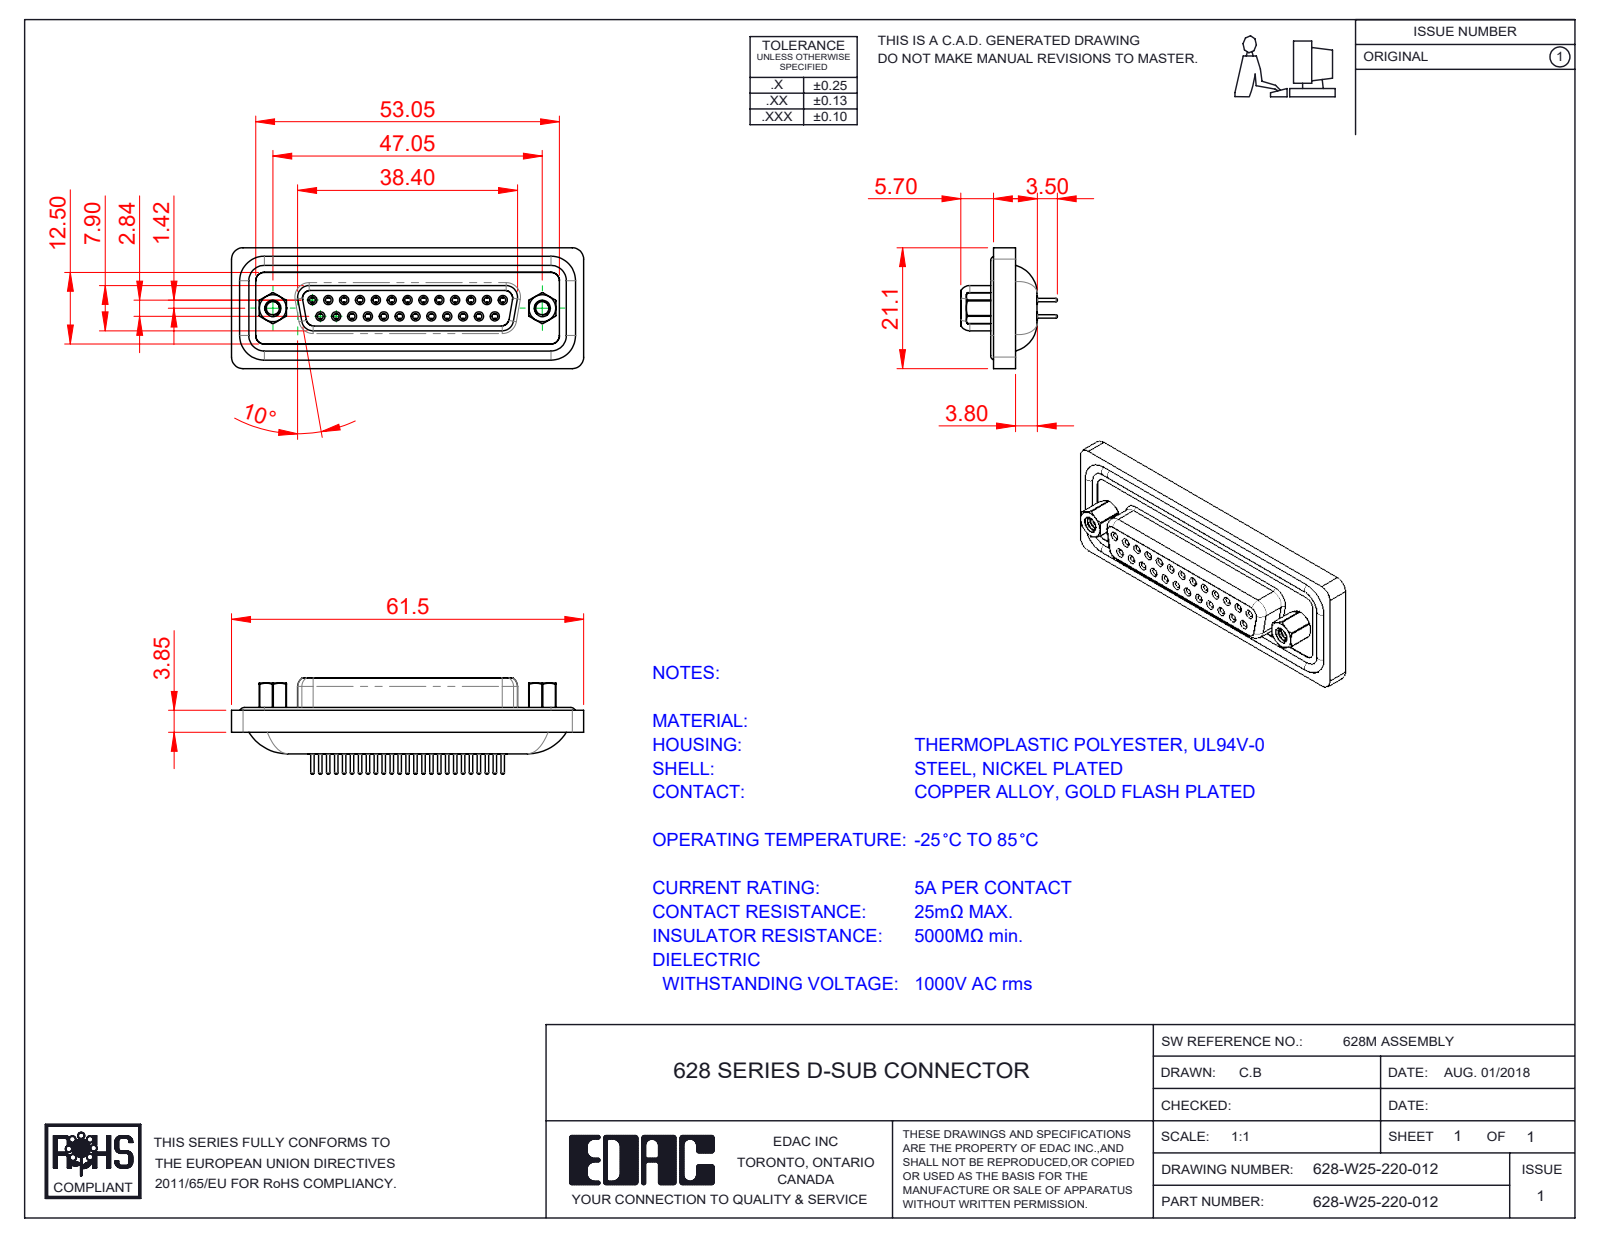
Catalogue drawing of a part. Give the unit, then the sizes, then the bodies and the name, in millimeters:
Units: millimetres
Overall size (bounding box): 61.5 × 21.1 × 16.85
Round holes (diameter × count): ⌀1 ×25, ⌀1.1 ×25, ⌀1.5 ×25, ⌀1.7 ×25, ⌀1.8 ×25, ⌀2 ×25, ⌀2.26 ×2, ⌀2.29 ×2, ⌀4 ×2, ⌀4.8 ×2, ⌀5 ×2
Round bosses / shafts (diameter × count): ⌀1.6 ×29, ⌀2.2 ×25, ⌀0.6 ×25, ⌀4.9 ×2, ⌀2.79 ×2
Partial cylindrical surfaces — rounded edges, fillets, slot ends (radius × count): R2 ×16, R1.5 ×14, R1.35 ×8, R2.7 ×6, R0.5 ×4, R0.9 ×4, R1.6 ×4, R1.75 ×4
Main face-to-face distances: 0.4, 7.45, 1.1, 2.75, 7.5, 3.75, 13.65, 0.5, 8.45, 6.2
Hole centre spacings: 3.16, 2.77, 5.54, 8.31, 11.08, 13.85, 16.62, 5.03
Volume: 8 488 mm³ · Surface area: 13 359 mm²
Bodies: 33 solids, 1848 faces (476 planar, 745 cylindrical, 627 other)
Part name (STEP PRODUCT): 628W Housing_25 Contacts; 628W Contact Row 1_20; 628W Shell Front_25 Contacts; 628W Contact Row 2_20 (+4 more)
STEP written by: SolidWorks 2020 (CONFIG_CONTROL_DESIGN)
